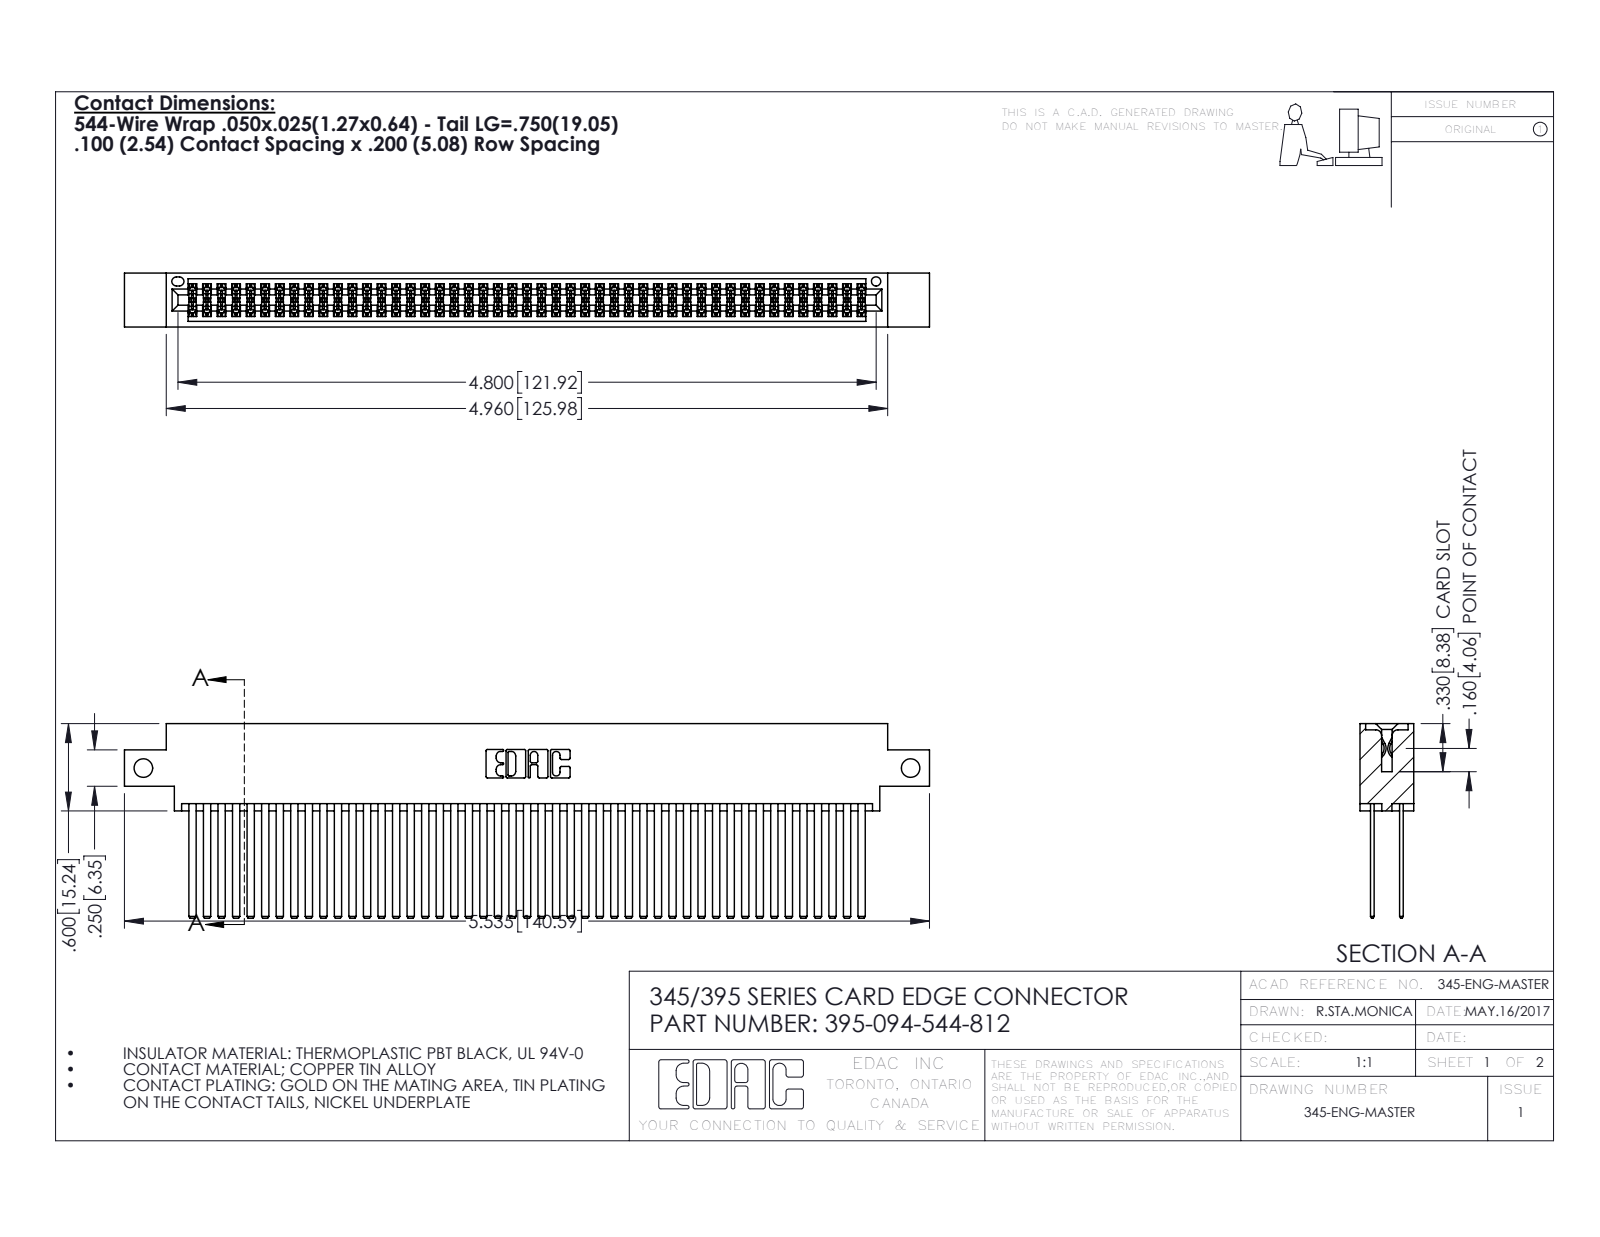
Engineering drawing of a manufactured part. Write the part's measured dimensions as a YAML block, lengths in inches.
part_name: "395-094-544-812; 345 Part_0.170 Offset - Side Mount; 345-292-001_345-293-144"
step_written_by: "SolidWorks 2016 (CONFIG_CONTROL_DESIGN)"
units: inches
bodies: {solids: 95, faces: 4266, planar: 2810, cylindrical: 1456, other: 0}
overall_size: [5.535, 1.337, 0.37]
volume: 0.904
surface_area: 40.1
round_holes:
  - {diameter: 0.128, count: 2}
  - {diameter: 0.064, count: 1}
partial_cylinders:
  - {radius: 0.006, count: 141}
  - {radius: 0.01, count: 22}
  - {radius: 0.007, count: 6}
  - {radius: 0.031, count: 6}
  - {radius: 0.026, count: 3}
  - {radius: 0.014, count: 2}
  - {radius: 0.019, count: 2}
  - {radius: 0.022, count: 2}
face_to_face_distances: [0.2, 0.025, 0.298, 0.072, 0.098, 0.272, 0.225, 0.175, 0.37, 0.15]
hole_center_spacings: [5.275]
